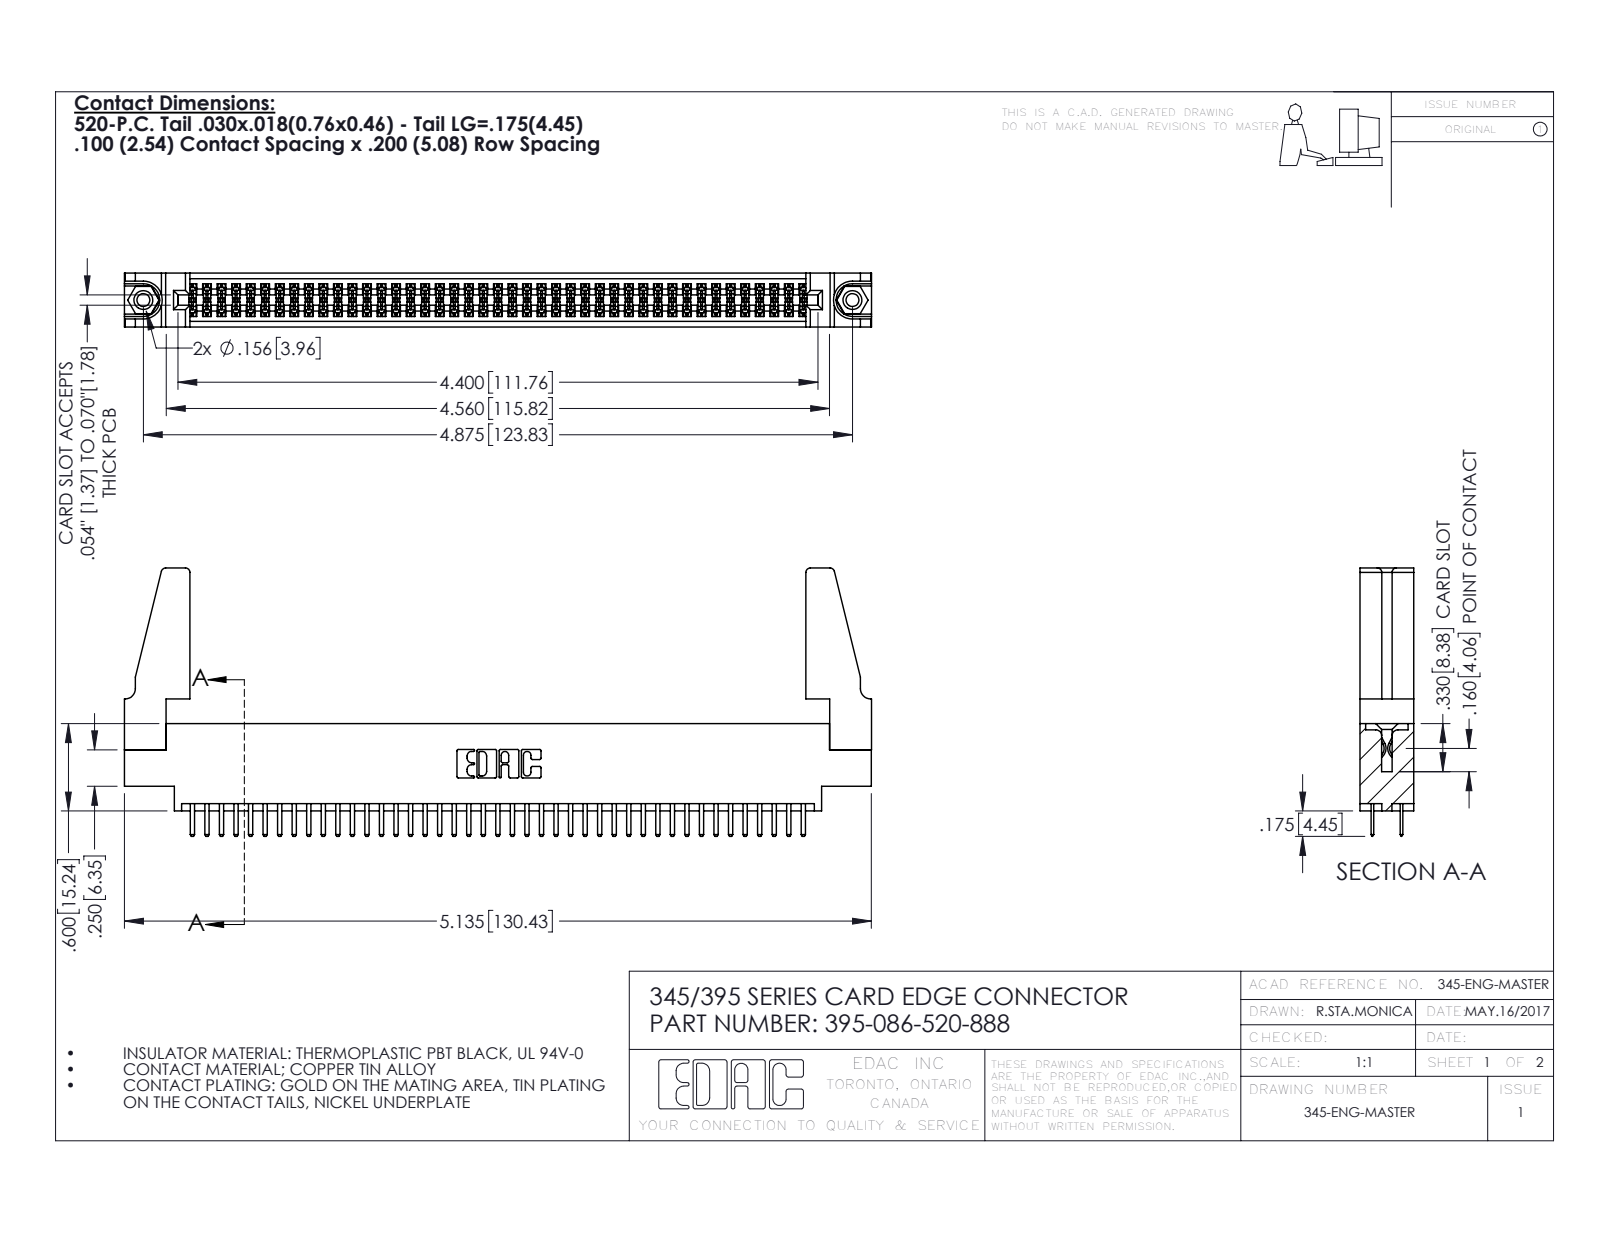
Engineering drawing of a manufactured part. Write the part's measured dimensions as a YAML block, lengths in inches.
part_name: "345-250-001_345-250-001-102; 345-220-078_345-220-088; 345-292-001_345-293-120; 345 Part_0.170 Offset - 0.156 Dia-TH (+1 more)"
step_written_by: "SolidWorks 2016 (CONFIG_CONTROL_DESIGN)"
units: inches
bodies: {solids: 91, faces: 4898, planar: 3166, cylindrical: 1716, other: 16}
overall_size: [5.136, 1.845, 0.37]
volume: 0.963
surface_area: 33.68
round_holes:
  - {diameter: 0.089, count: 2}
  - {diameter: 0.125, count: 2}
  - {diameter: 0.156, count: 2}
  - {diameter: 0.064, count: 1}
round_bosses_or_shafts:
  - {diameter: 0.155, count: 2}
partial_cylinders:
  - {radius: 0.006, count: 129}
  - {radius: 0.01, count: 90}
  - {radius: 0.01, count: 22}
  - {radius: 0.03, count: 8}
  - {radius: 0.007, count: 6}
  - {radius: 0.031, count: 6}
  - {radius: 0.026, count: 3}
  - {radius: 0.014, count: 2}
face_to_face_distances: [0.072, 0.298, 0.37, 0.2, 0.098, 0.272, 0.025, 0.225, 0.022, 0.175]
hole_center_spacings: [0.27, 4.639, 4.875]
